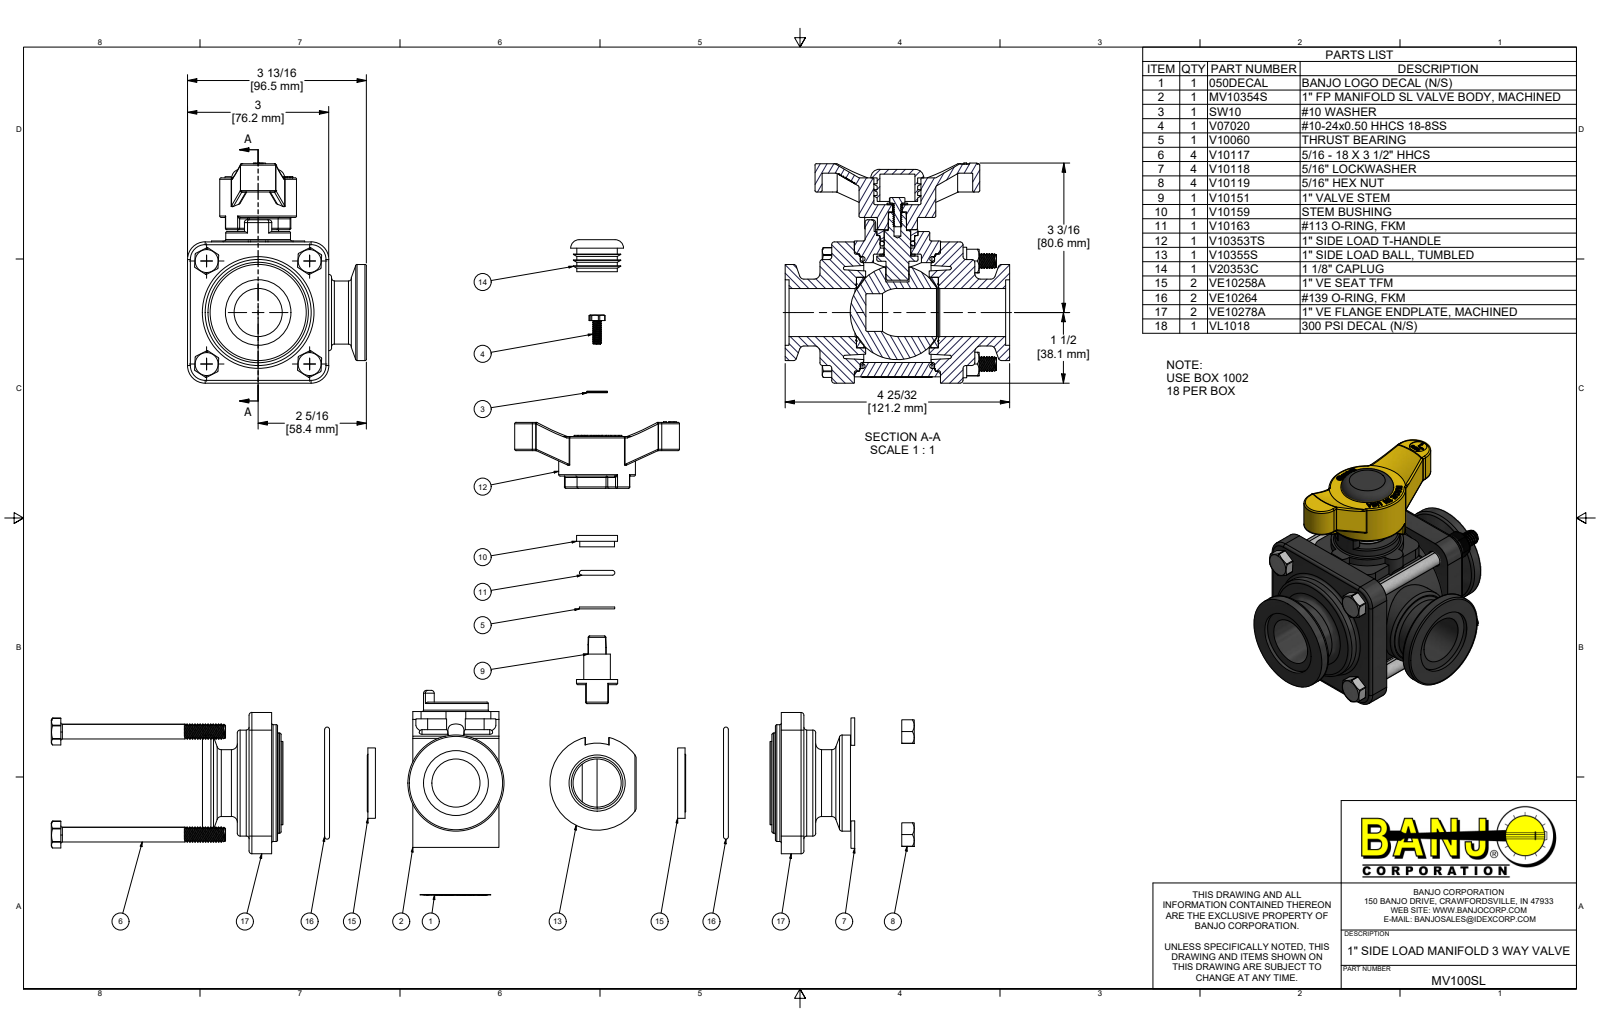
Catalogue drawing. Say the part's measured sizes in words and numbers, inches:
The part is named "MV100SL; VE10278A; V10278X; V10353TS (+8 more)". Its 3-D file was written by "Autodesk Inventor 2019 (AUTOMOTIVE_DESIGN)". It is 29 solids with 2914 faces: 1246 planar, 681 cylindrical and 987 other. Overall it measures 4.77 by 4.675 by 3.8 inches. Its volume is 23.99 cubic inches and its surface area 219.3 square inches. Round holes: 4 of diameter 0.252, 4 of diameter 0.322, 4 of diameter 0.35, 3 of diameter 1.02, 1 of diameter 0.091, 1 of diameter 0.128, 1 of diameter 0.145, 1 of diameter 0.203, 1 of diameter 0.21, 1 of diameter 0.227, 1 of diameter 0.321, 1 of diameter 0.375. Round bosses or shafts: 60 of diameter 0.268, 4 of diameter 0.583, 4 of diameter 0.313, 2 of diameter 2.04, 1 of diameter 2.73, 1 of diameter 2.48, 1 of diameter 2.25, 1 of diameter 2.124. Partial cylindrical surfaces (rounded edges, fillets, slot ends): 58 of radius 0.03, 12 of radius 0.031, 12 of radius 0.062, 10 of radius 0.06, 10 of radius 0.375, 8 of radius 0.134, 4 of radius 0.21, 4 of radius 0.25. The main face-to-face distances are 0.48, 2.31, 3, 1.83, 2.79, 0.74, 1.47, 0.99, 3.3, 3.78. The hole center spacings are 1.547, 2.188, 3.094, 0.51, 0.663, 0.708, 1.533, 1.83.
